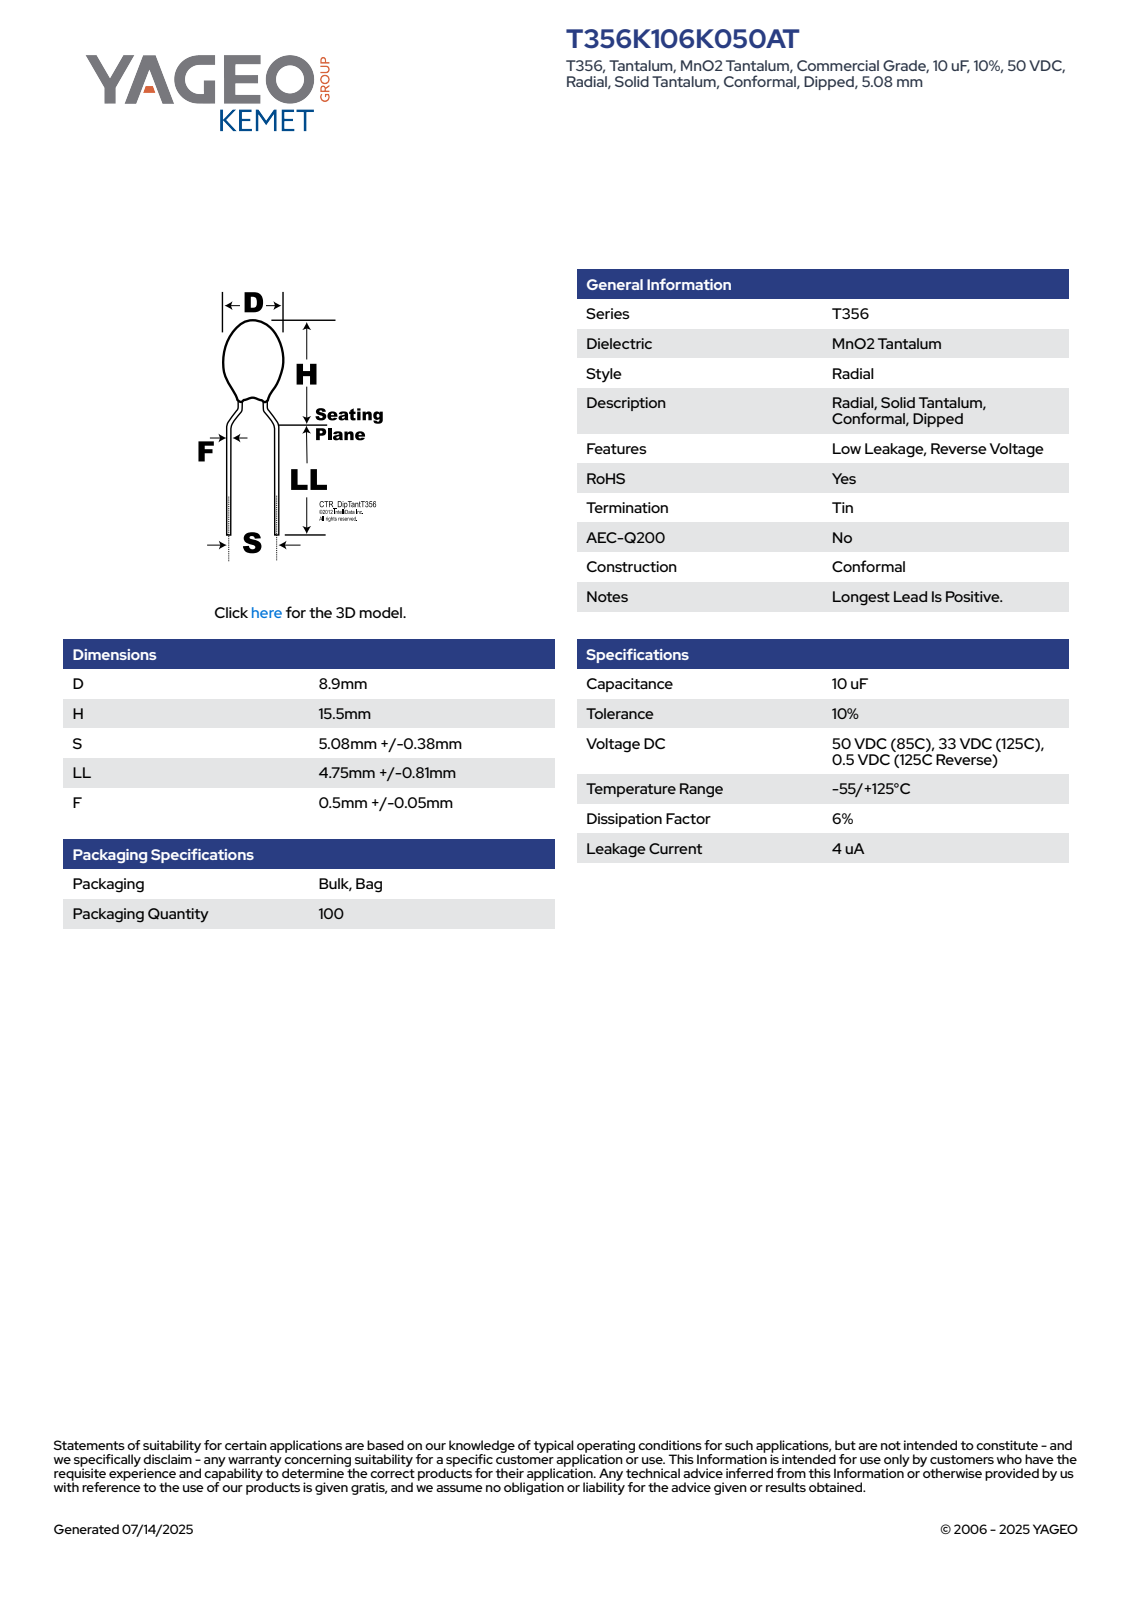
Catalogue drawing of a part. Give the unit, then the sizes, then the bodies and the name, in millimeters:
Units: millimetres
Overall size (bounding box): 21.06 × 8.9 × 8.9
Round bosses / shafts (diameter × count): ⌀0.55 ×6, ⌀8.9 ×1
Partial cylindrical surfaces — rounded edges, fillets, slot ends (radius × count): R4.44 ×1
Main face-to-face distances: 10.81, 10.25, 21.06, 17.28, 7.03, 3.78, 16.07, 5.82, 1.21, 4.99
Volume: 586 mm³ · Surface area: 390 mm²
Bodies: 1 solid, 96 faces (27 planar, 18 cylindrical, 51 other)
Part name (STEP PRODUCT): CTR_T356_D8.9H15.5S5.08LL5.56F0.55
STEP written by: SolidWorks 2014 (AUTOMOTIVE_DESIGN)
